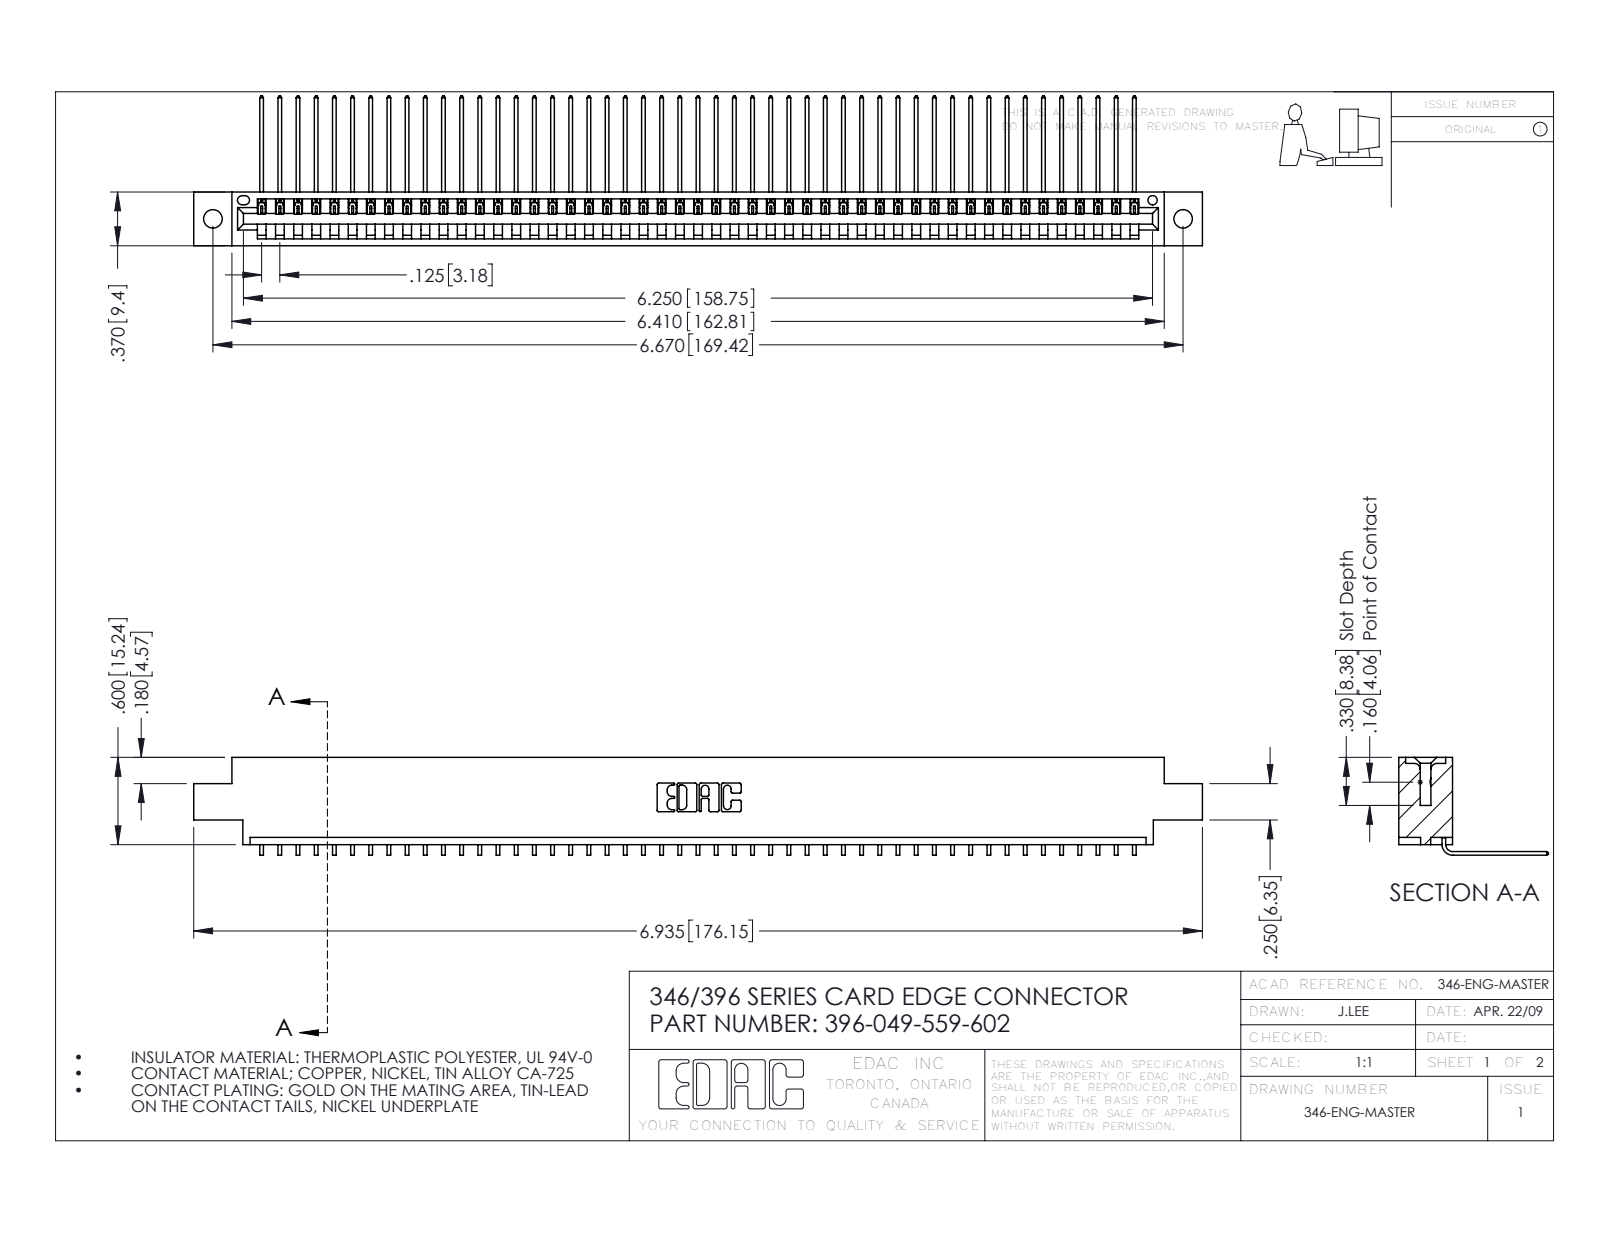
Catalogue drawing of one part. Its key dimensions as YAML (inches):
part_name: "345-292-001_558 559 Tail - 1; 346 Part_0.170 Offset - 0.128 Dia; 396-049-559-602"
step_written_by: "SolidWorks 2016 (CONFIG_CONTROL_DESIGN)"
units: inches
bodies: {solids: 50, faces: 3066, planar: 2138, cylindrical: 928, other: 0}
overall_size: [6.935, 1.03, 0.673]
volume: 1.03
surface_area: 34.16
round_holes:
  - {diameter: 0.128, count: 2}
  - {diameter: 0.064, count: 1}
partial_cylinders:
  - {radius: 0.006, count: 98}
  - {radius: 0.01, count: 22}
  - {radius: 0.007, count: 6}
  - {radius: 0.031, count: 6}
  - {radius: 0.026, count: 3}
  - {radius: 0.031, count: 2}
  - {radius: 0.04, count: 2}
  - {radius: 0.014, count: 1}
face_to_face_distances: [0.048, 0.322, 0.37, 0.025, 0.25, 0.072, 0.298, 0.148, 0.222, 0.1]
hole_center_spacings: [0.246, 6.461, 6.67]
